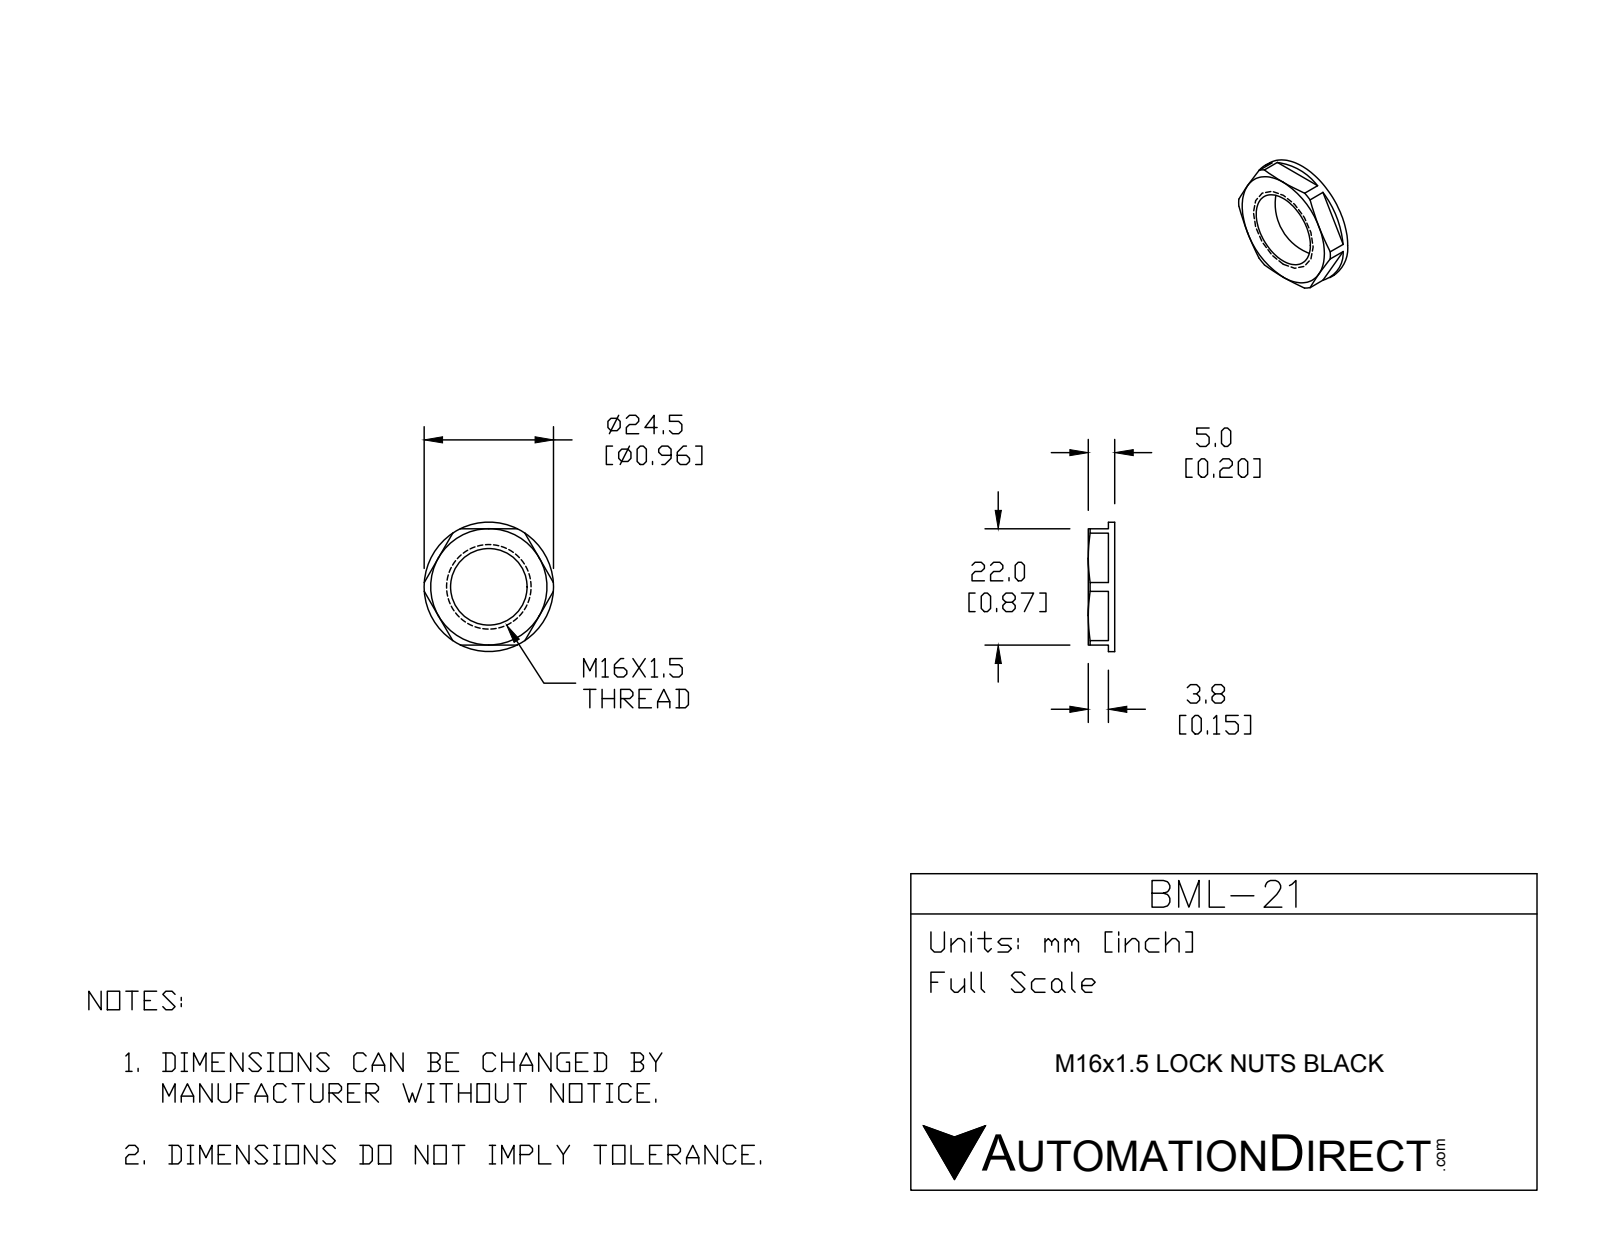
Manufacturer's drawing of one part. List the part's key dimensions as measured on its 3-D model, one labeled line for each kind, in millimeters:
Part name (STEP PRODUCT): BML-21
STEP written by: SolidWorks 2015 (CONFIG_CONTROL_DESIGN)
Units: millimetres
Bodies: 1 solid, 34 faces (17 planar, 10 cylindrical, 7 other)
Overall size (bounding box): 24.5 × 24.5 × 5
Volume: 1 318 mm³ · Surface area: 1 211 mm²
Round holes (diameter × count): ⌀1.5 ×3, ⌀14.5 ×1
Round bosses / shafts (diameter × count): ⌀24.5 ×1
Main face-to-face distances: 5, 22, 1.2, 3.8, 0.9, 4.7
Hole centre spacings: 10.8, 18.7
